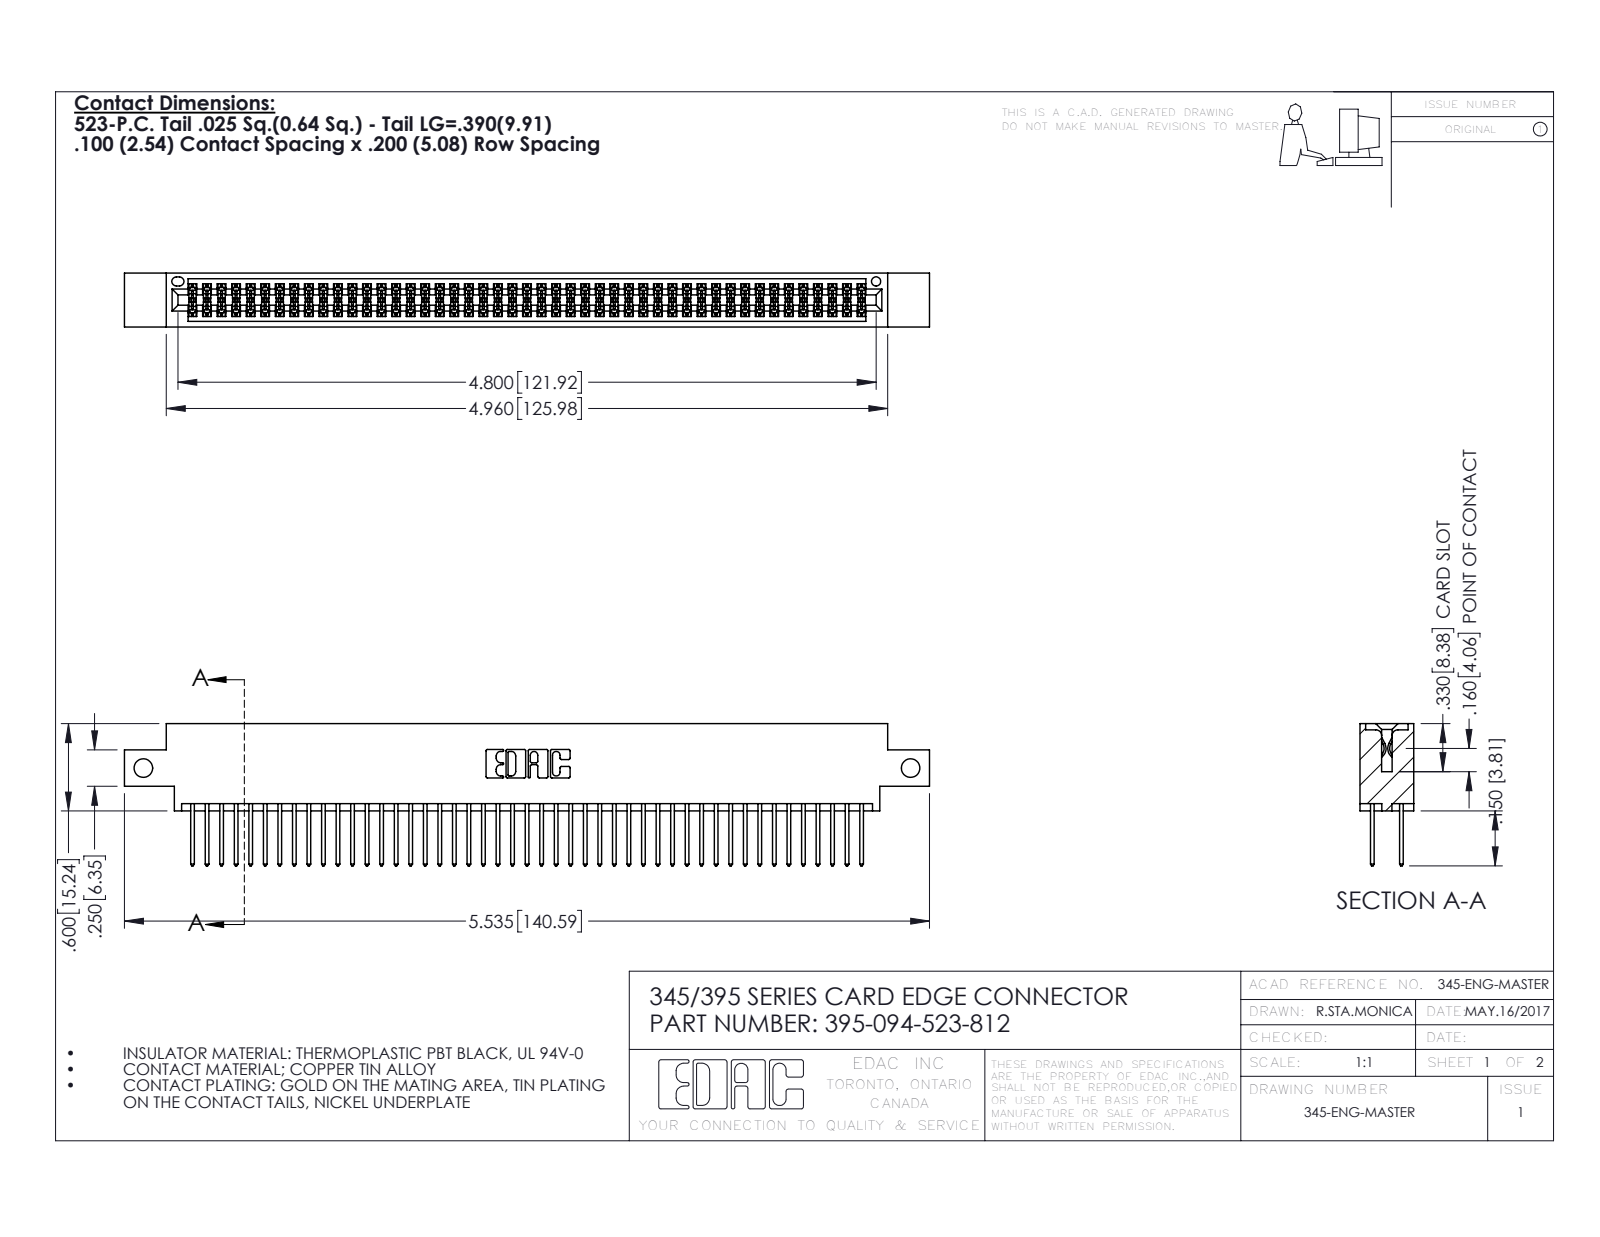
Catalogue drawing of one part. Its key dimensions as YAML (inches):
part_name: "345 Part_0.170 Offset - Side Mount; 345-292-001_345-293-123; 395-094-523-812"
step_written_by: "SolidWorks 2016 (CONFIG_CONTROL_DESIGN)"
units: inches
bodies: {solids: 95, faces: 4830, planar: 3186, cylindrical: 1644, other: 0}
overall_size: [5.535, 0.977, 0.37]
volume: 0.836
surface_area: 32.88
round_holes:
  - {diameter: 0.128, count: 2}
  - {diameter: 0.064, count: 1}
partial_cylinders:
  - {radius: 0.006, count: 141}
  - {radius: 0.01, count: 94}
  - {radius: 0.01, count: 22}
  - {radius: 0.007, count: 6}
  - {radius: 0.031, count: 6}
  - {radius: 0.026, count: 3}
  - {radius: 0.014, count: 2}
  - {radius: 0.019, count: 2}
face_to_face_distances: [0.298, 0.072, 0.2, 0.098, 0.272, 0.025, 0.37, 0.225, 0.175, 0.149]
hole_center_spacings: [5.275]
